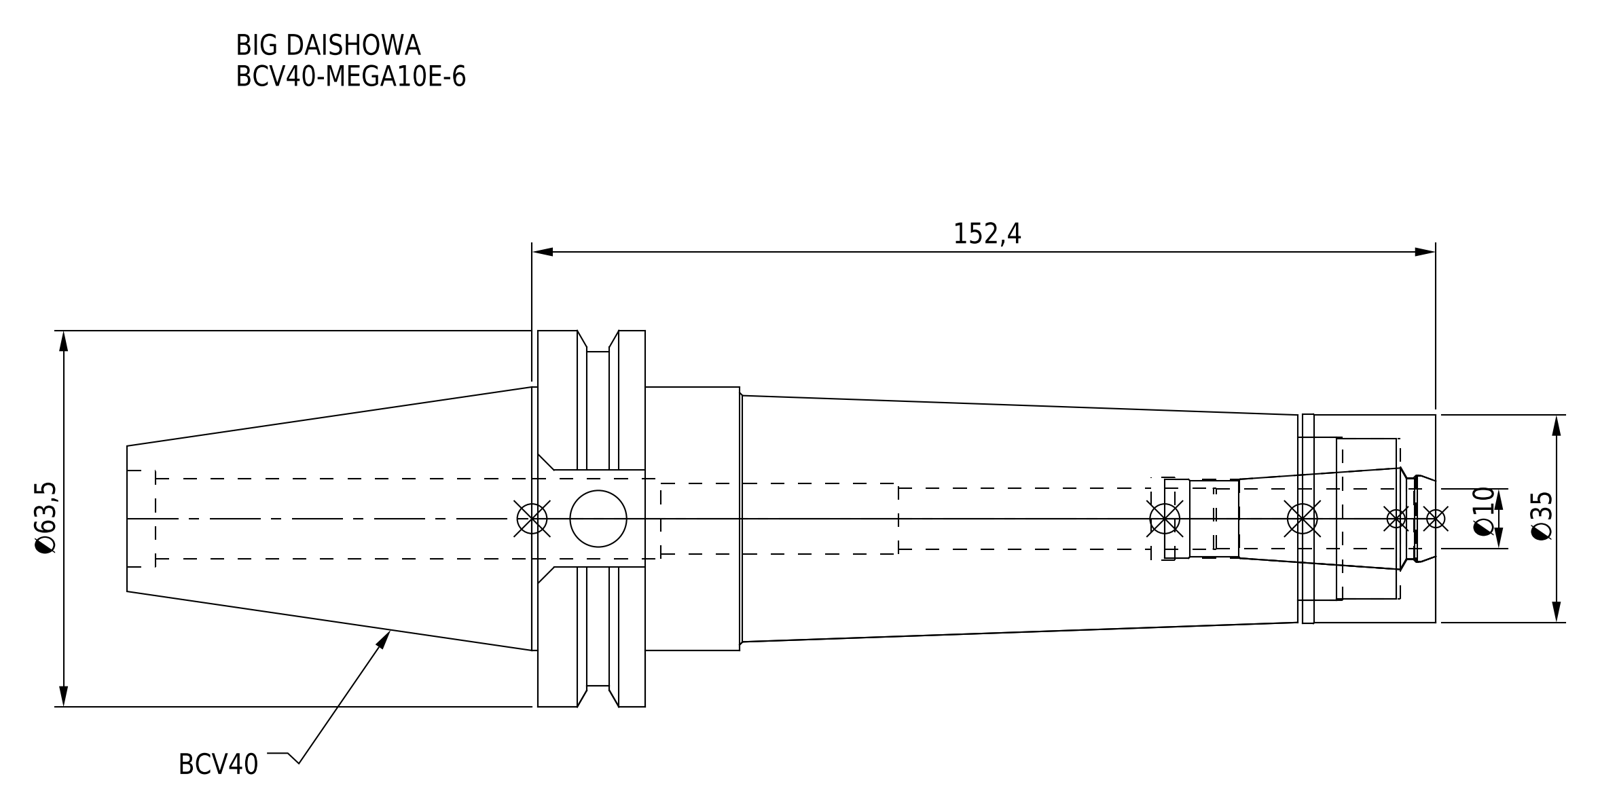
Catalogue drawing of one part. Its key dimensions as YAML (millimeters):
part_name: "MEN10_1.stp; DXF_TEMP_ASSY_ASM_4_ASM.stp; BCV40-MEGA10E-6; BCV40-MEGA10E-6-100-FreeParts (+3 more)"
step_written_by: "SolidWorks 2019 (CONFIG_CONTROL_DESIGN)"
units: millimeters
bodies: {solids: 2, faces: 93, planar: 31, cylindrical: 42, other: 20}
overall_size: [220.65, 63.5, 61.35]
volume: 242514
surface_area: 45763
round_holes:
  - {diameter: 9.53, count: 1}
  - {diameter: 10.4, count: 1}
  - {diameter: 12, count: 1}
  - {diameter: 13.3, count: 1}
  - {diameter: 13.6, count: 1}
  - {diameter: 13.8, count: 1}
  - {diameter: 13.9, count: 1}
  - {diameter: 14.7, count: 1}
  - {diameter: 16.32, count: 1}
  - {diameter: 27, count: 1}
  - {diameter: 27.5, count: 1}
round_bosses_or_shafts:
  - {diameter: 63.5, count: 1}
  - {diameter: 56.36, count: 1}
  - {diameter: 44.45, count: 1}
  - {diameter: 35.3, count: 1}
  - {diameter: 35, count: 1}
face_to_face_distances: [18.05, 133.35, 151.4, 6, 22.5, 110.85, 128.9, 23.3, 0.8, 110.05]
